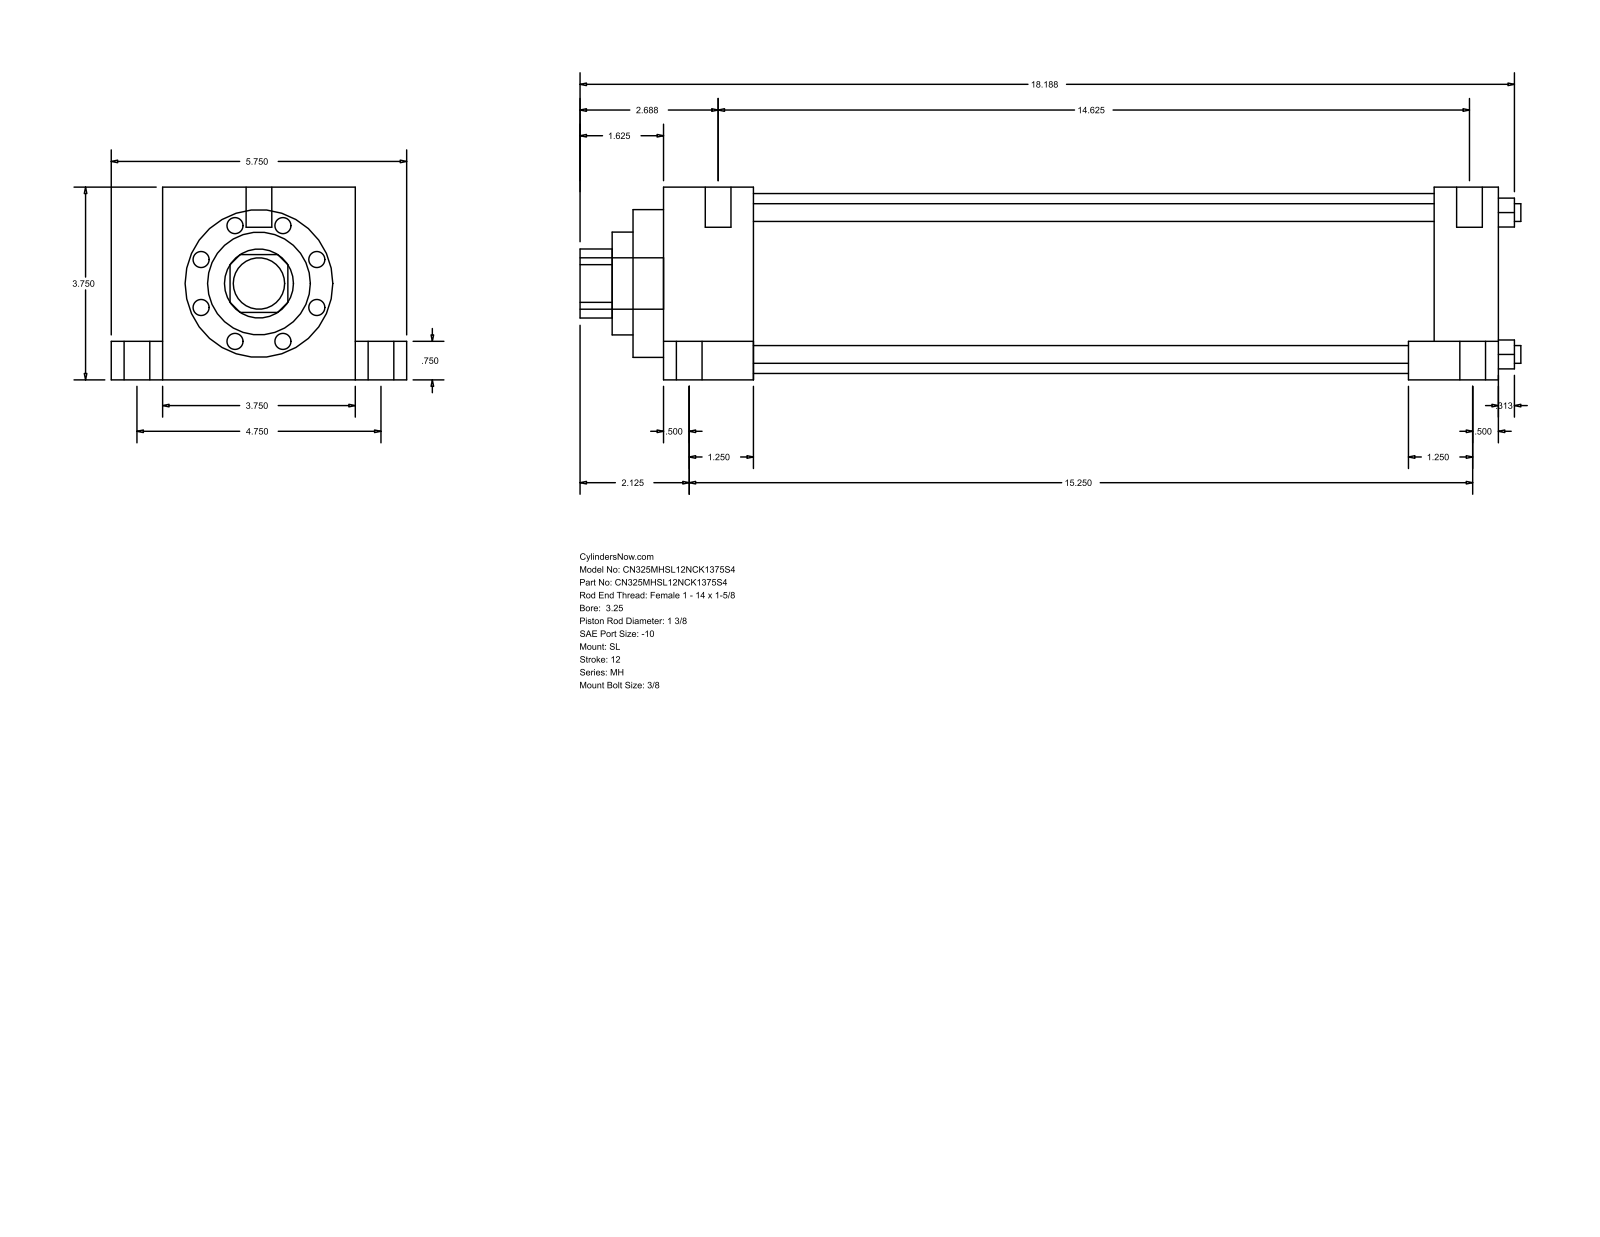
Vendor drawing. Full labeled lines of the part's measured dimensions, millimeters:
Part name (STEP PRODUCT): MH_SL__0325_1.375
STEP written by: GSSL Pune (CONFIG_CONTROL_DESIGN)
Units: millimetres
Bodies: 0 solids, 110 faces (77 planar, 33 cylindrical, 0 other)
Overall size (bounding box): 465.14 × 146.05 × 95.25
Round holes (diameter × count): ⌀8.76 ×4, ⌀34.92 ×1, ⌀50.8 ×1, ⌀73.03 ×1, ⌀88.9 ×1
Round bosses / shafts (diameter × count): ⌀12.7 ×6, ⌀19.05 ×4, ⌀5.56 ×4, ⌀25.4 ×1
Partial cylindrical surfaces — rounded edges, fillets, slot ends (radius × count): R17.06 ×1
Main face-to-face distances: 95.24, 412.75, 44.45, 368.3, 25.41, 120.65, 19.05, 76.19, 381, 336.55
Hole centre spacings: 49.57, 70.1, 99.14
